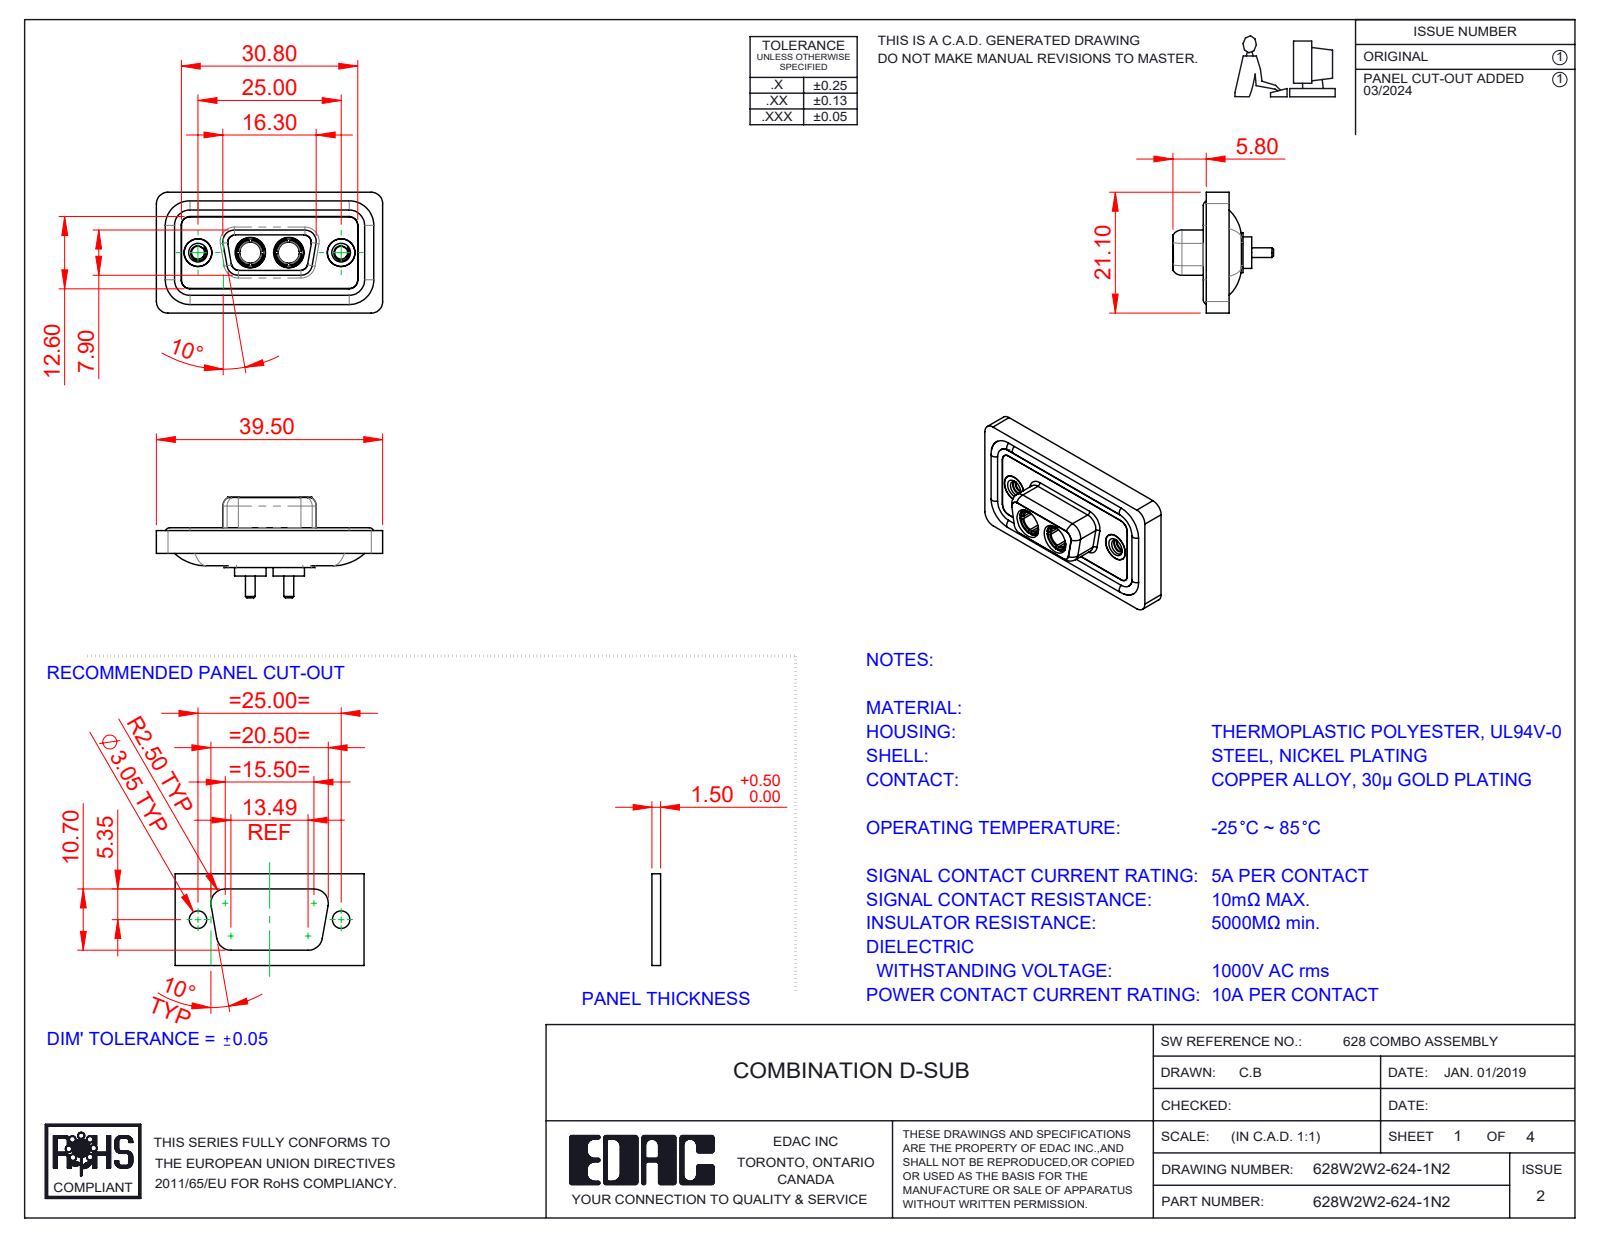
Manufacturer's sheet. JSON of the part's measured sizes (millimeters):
{"part_name": "628Combo Threaded Rivet_2; 628W2W2-624-1N2; 628Combo Waterproof Housing_09 Contacts; 628Combo Housing_2W2 (+3 more)", "step_written_by": "SolidWorks 2023 (CONFIG_CONTROL_DESIGN)", "units": "millimeters", "bodies": {"solids": 11, "faces": 534, "planar": 163, "cylindrical": 234, "other": 137}, "overall_size": [39.5, 21.1, 17.55], "volume_mm3": 4683, "surface_area_mm2": 7611, "round_holes": [[4.85, 4], [2.26, 2], [3.7, 2], [4, 2], [4.05, 2], [5, 2], [5.3, 2]], "round_bosses_or_shafts": [[1.6, 4], [5.5, 2], [5.2, 2], [4.96, 2], [4.95, 2], [4.8, 2], [4.75, 2], [3.75, 2]], "partial_cylinders_radius": [[1.5, 22], [2, 18], [1.35, 8], [1.6, 8], [0.25, 4], [0.5, 4], [0.6, 4], [0.65, 4]], "face_to_face_distances": [0.4, 1.8, 1.1, 2.9, 0.5, 1.6, 5.65, 1.5, 7.45, 5.35], "hole_center_spacings": [9.14, 15.86, 6.72, 25]}
